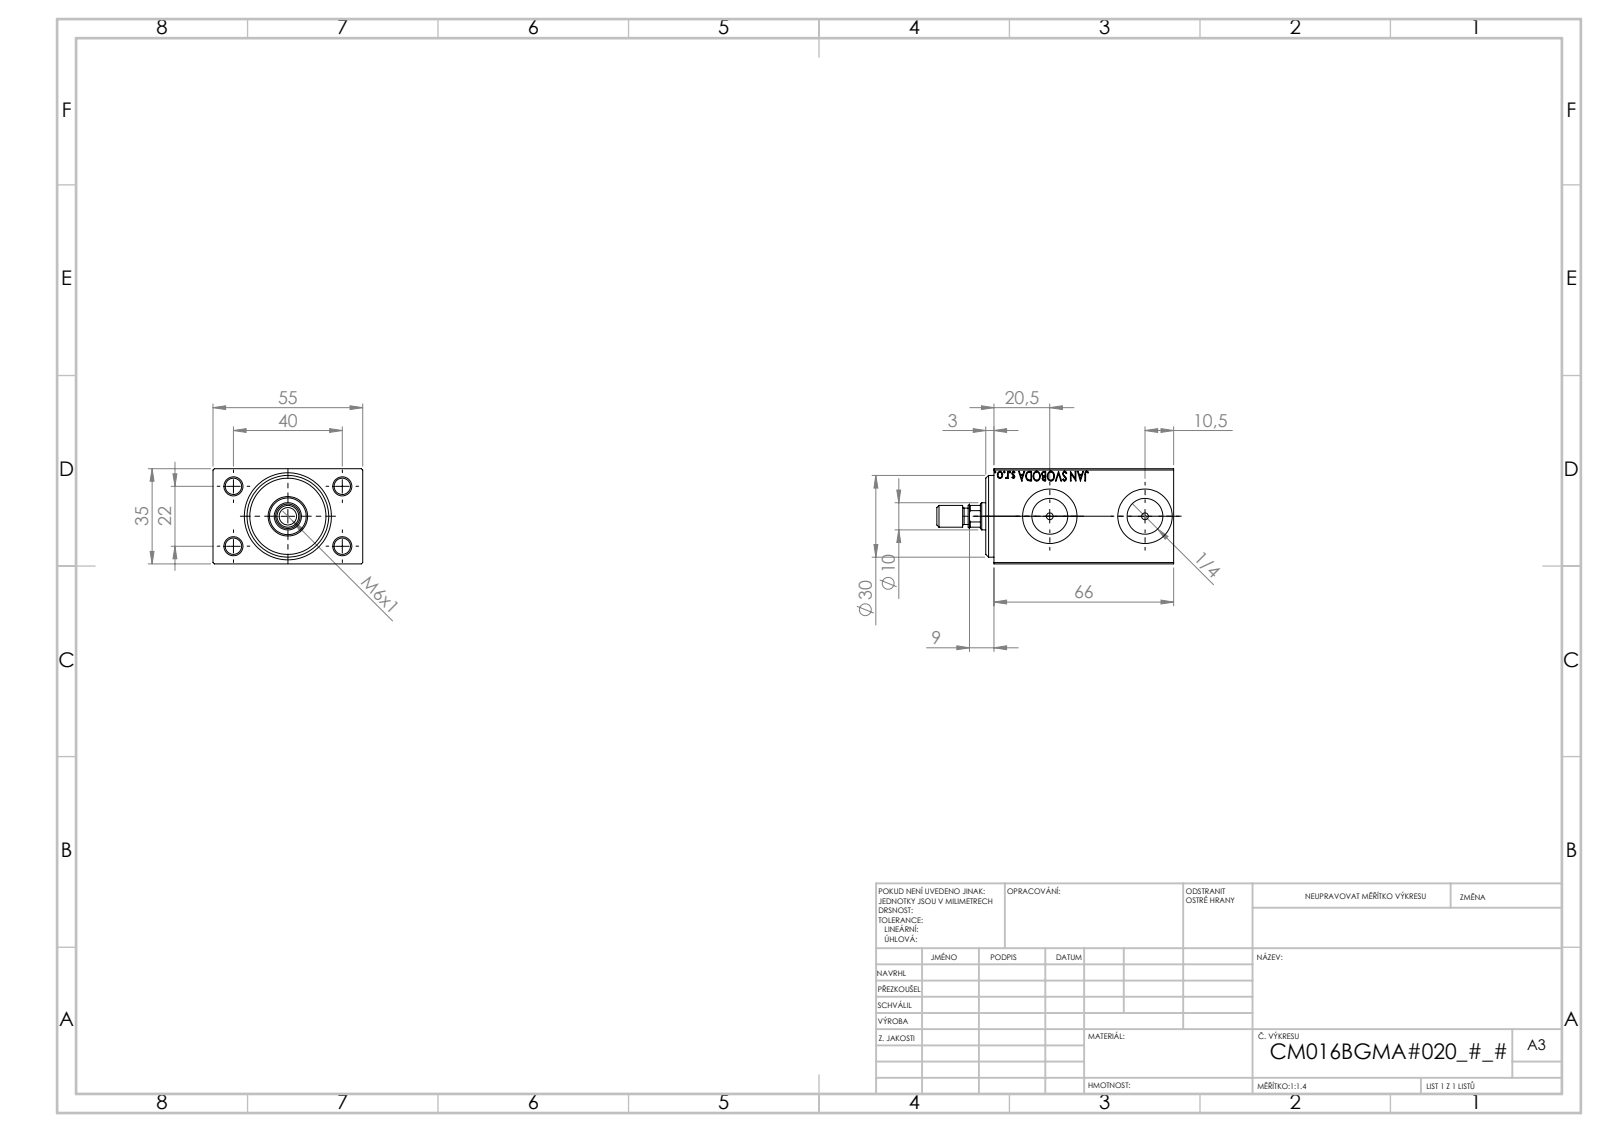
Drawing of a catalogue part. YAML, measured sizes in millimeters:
part_name: "V450CM_MALE_METRIC; V450CM_B_VCP; V450CM_VC_B; V450CM_B_Body"
step_written_by: "SolidWorks 2019 (CONFIG_CONTROL_DESIGN)"
units: millimeters
bodies: {solids: 4, faces: 895, planar: 405, cylindrical: 58, other: 432}
overall_size: [87, 55, 35]
volume: 121099
surface_area: 28089
round_holes:
  - {diameter: 6, count: 4}
  - {diameter: 2.5, count: 2}
  - {diameter: 13.16, count: 2}
  - {diameter: 20, count: 2}
  - {diameter: 4.5, count: 1}
  - {diameter: 10, count: 1}
  - {diameter: 13.5, count: 1}
  - {diameter: 14.5, count: 1}
  - {diameter: 16, count: 1}
  - {diameter: 18, count: 1}
  - {diameter: 30, count: 1}
round_bosses_or_shafts:
  - {diameter: 8, count: 1}
  - {diameter: 6, count: 1}
partial_cylinders:
  - {radius: 4.5, count: 1}
face_to_face_distances: [35, 55, 5, 61, 66, 8, 3, 69, 64, 56]
hole_center_spacings: [22.83, 22, 40, 45.65, 35]
